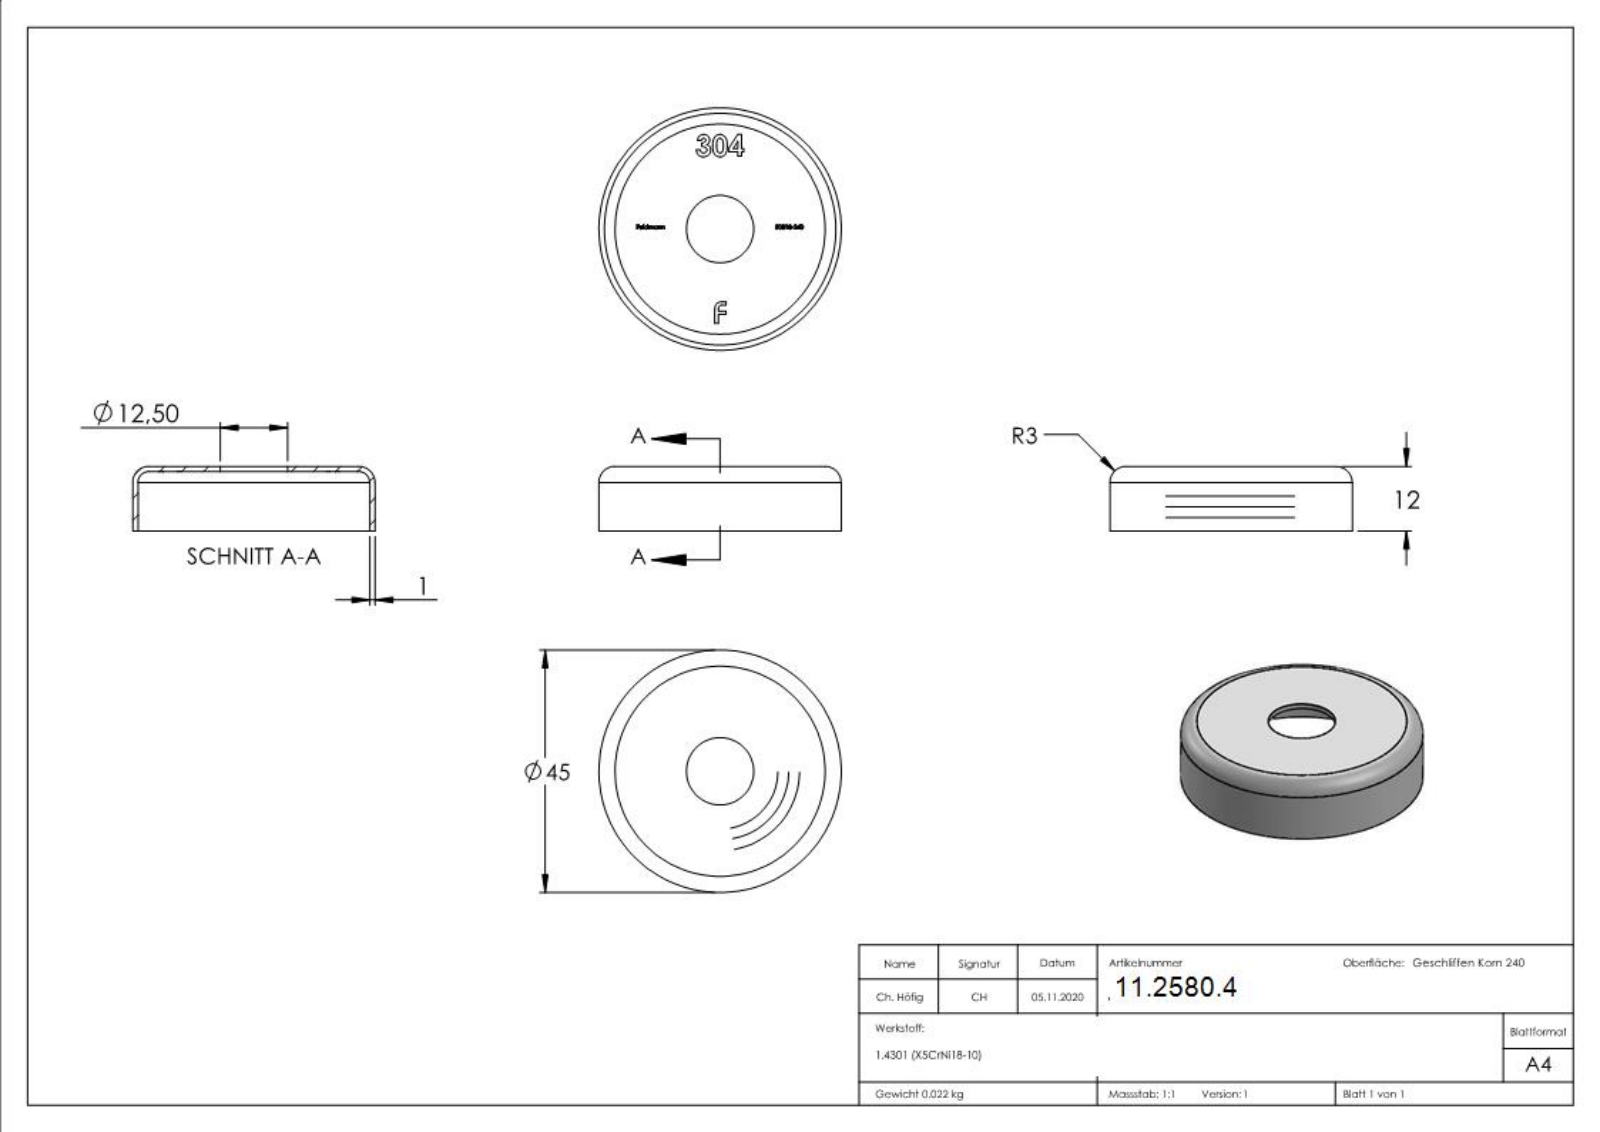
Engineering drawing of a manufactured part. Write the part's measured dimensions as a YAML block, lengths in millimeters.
part_name: "50818-240"
step_written_by: "SolidWorks 2018 (CONFIG_CONTROL_DESIGN)"
units: millimeters
bodies: {solids: 1, faces: 301, planar: 152, cylindrical: 6, other: 143}
overall_size: [45, 45, 12]
volume: 2834
surface_area: 5866
round_holes:
  - {diameter: 12.5, count: 1}
  - {diameter: 43, count: 1}
round_bosses_or_shafts:
  - {diameter: 45, count: 1}
face_to_face_distances: [1, 11, 12, 11.1, 0.9, 0.71, 5, 4.29, 0.58, 0.69]
